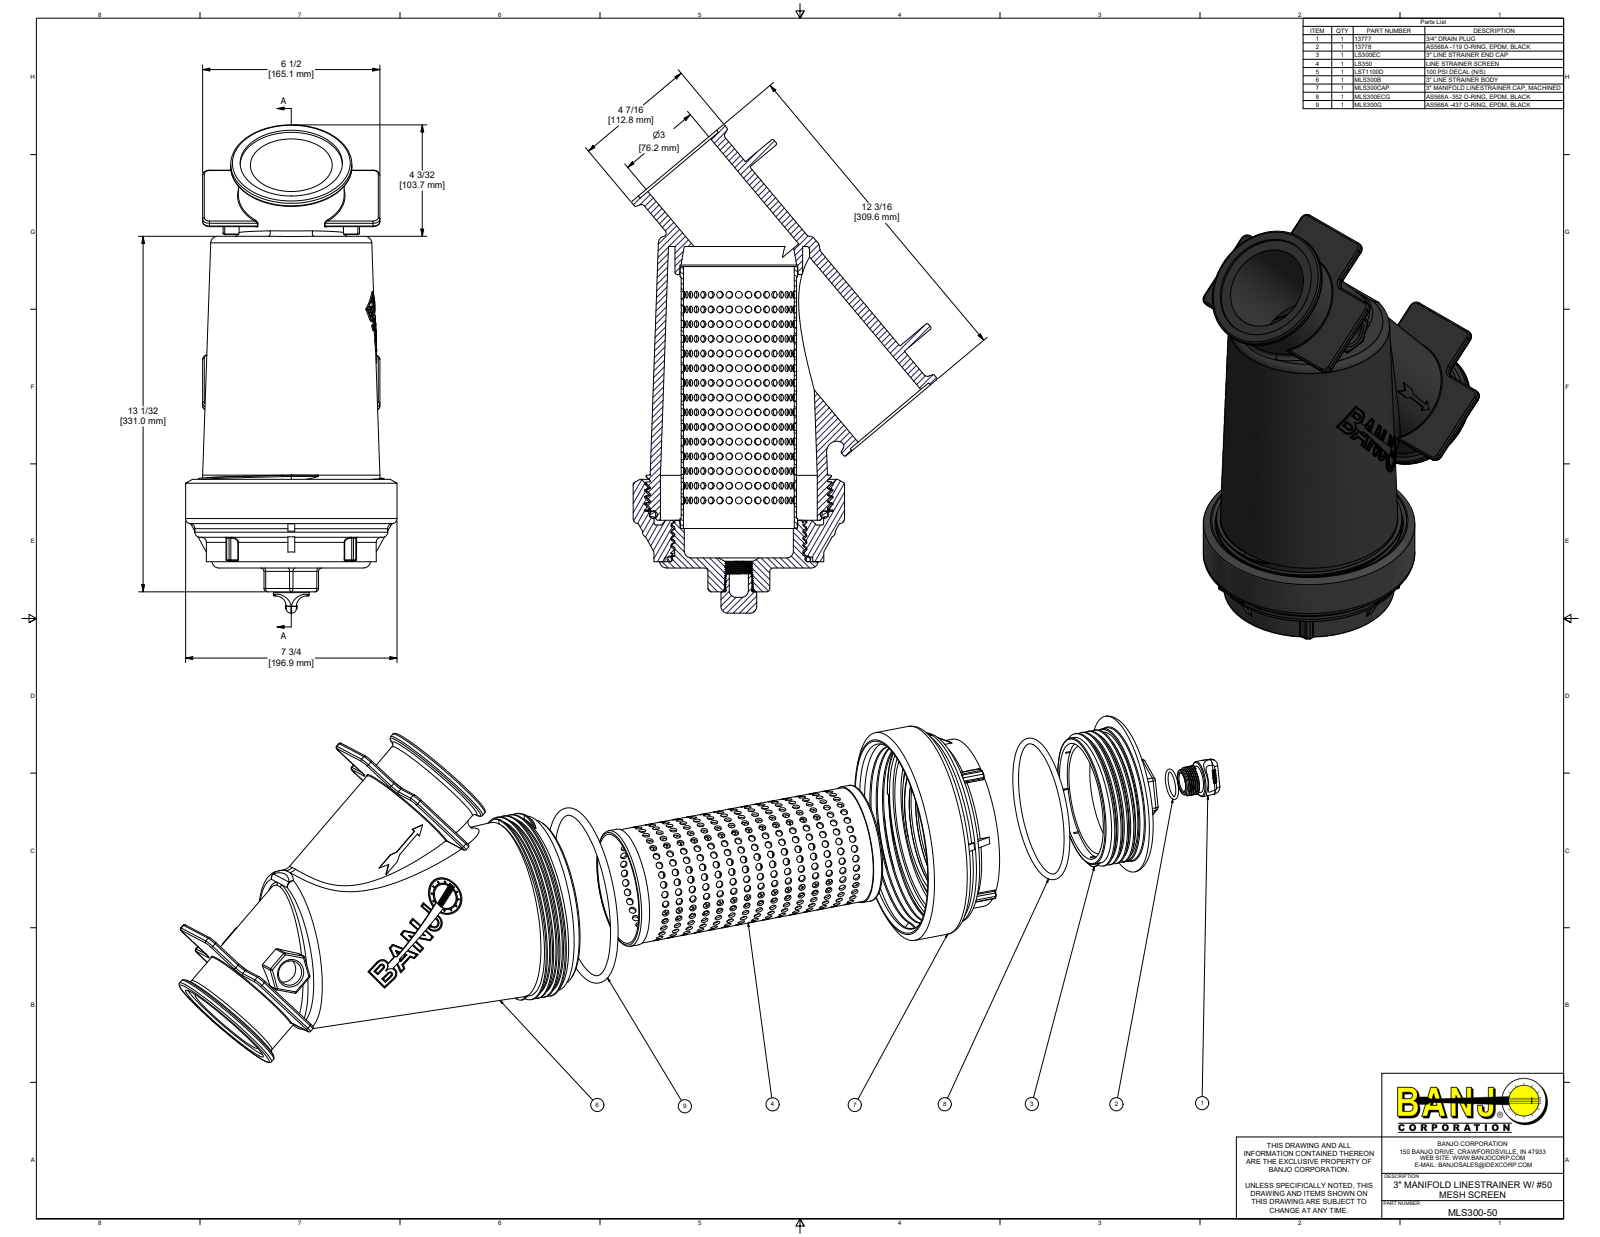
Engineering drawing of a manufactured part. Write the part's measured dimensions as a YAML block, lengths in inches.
part_name: "MLS300-50; MLS300B; LS300EC; LS300ECX (+7 more)"
step_written_by: "Autodesk Inventor 2022 (AUTOMOTIVE_DESIGN)"
units: inches
bodies: {solids: 8, faces: 1778, planar: 480, cylindrical: 824, other: 474}
overall_size: [17.836, 11.186, 7.75]
volume: 191.6
surface_area: 1269
round_holes:
  - {diameter: 0.25, count: 495}
  - {diameter: 3.75, count: 2}
  - {diameter: 0.7, count: 1}
  - {diameter: 0.817, count: 1}
  - {diameter: 0.91, count: 1}
  - {diameter: 1.154, count: 1}
  - {diameter: 3, count: 1}
  - {diameter: 4, count: 1}
  - {diameter: 4.063, count: 1}
  - {diameter: 4.317, count: 1}
  - {diameter: 4.32, count: 1}
  - {diameter: 4.729, count: 1}
round_bosses_or_shafts:
  - {diameter: 4.44, count: 2}
  - {diameter: 3.88, count: 2}
  - {diameter: 7.75, count: 1}
  - {diameter: 7.07, count: 1}
  - {diameter: 6.8, count: 1}
  - {diameter: 6.5, count: 1}
  - {diameter: 6.23, count: 1}
  - {diameter: 6.1, count: 1}
partial_cylinders:
  - {radius: 0.06, count: 46}
  - {radius: 0.03, count: 28}
  - {radius: 0.125, count: 18}
  - {radius: 0.25, count: 17}
  - {radius: 0.02, count: 8}
  - {radius: 0.09, count: 8}
  - {radius: 0.015, count: 6}
  - {radius: 0.071, count: 2}
face_to_face_distances: [0.25, 8.815, 0.23, 8.565, 9.065, 1.712, 1.462, 10.277, 10.527, 0.37]
hole_center_spacings: [1.077, 2.154, 0.538, 1.615, 2.692, 3.769, 0.539, 3.23]
